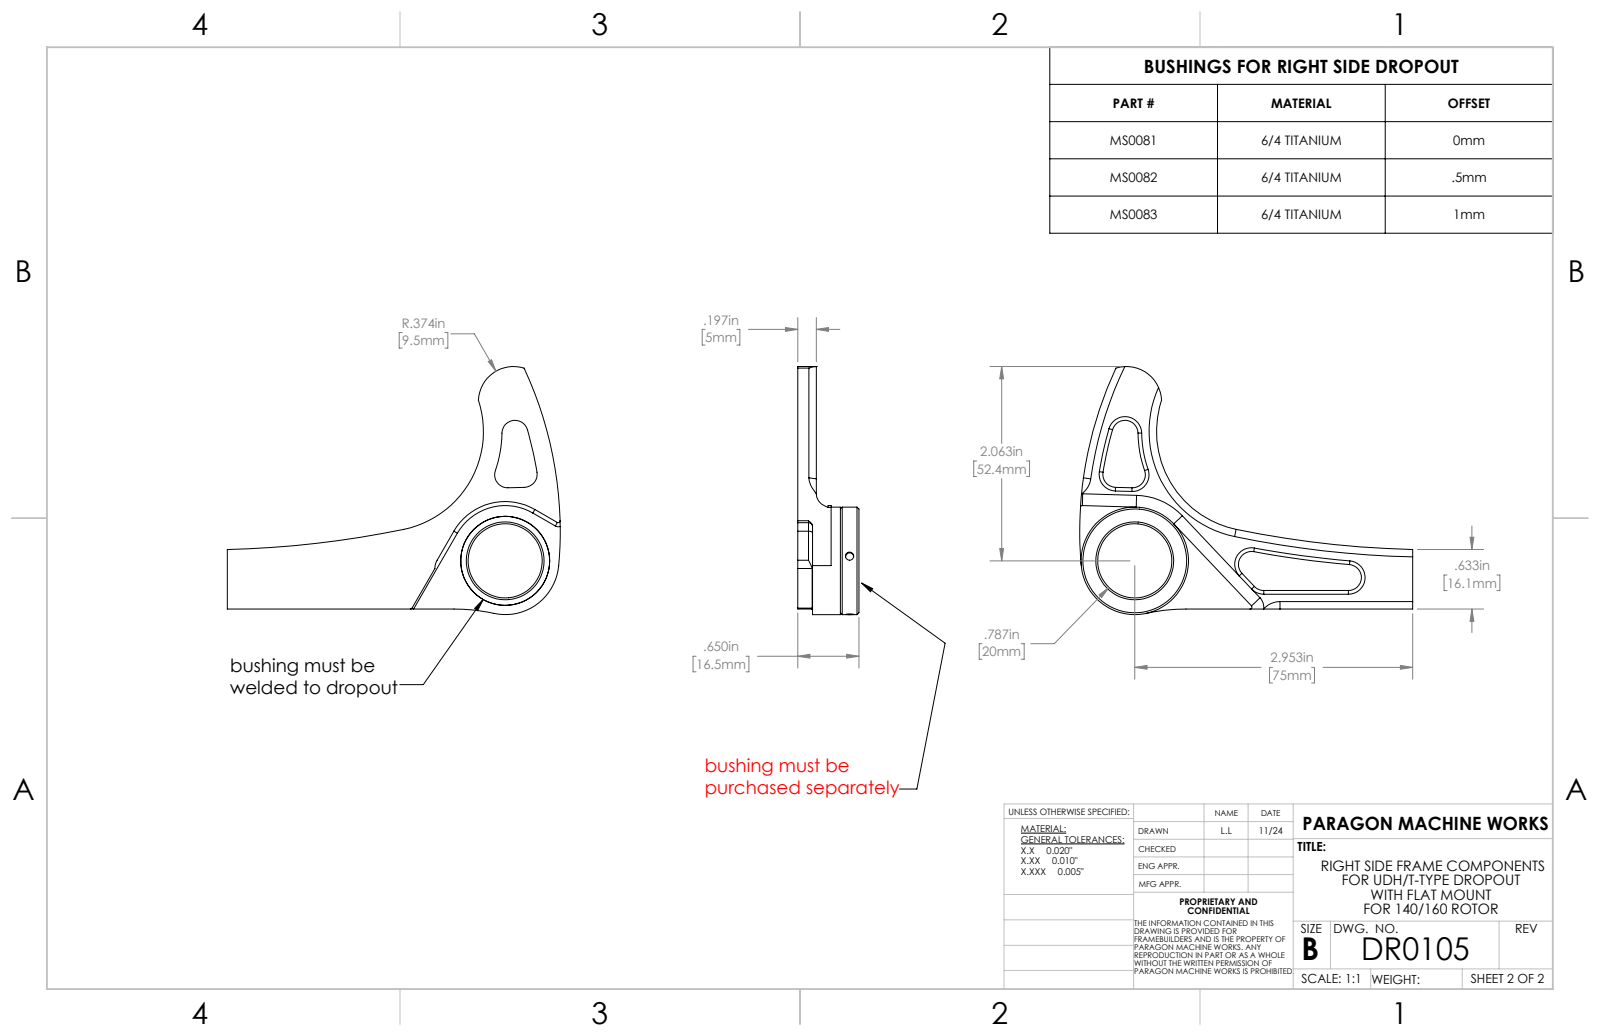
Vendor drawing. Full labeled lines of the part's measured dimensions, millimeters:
Part name (STEP PRODUCT): DR0102R
STEP written by: SolidWorks 2023 (AUTOMOTIVE_DESIGN)
Units: millimetres
Bodies: 1 solid, 74 faces (21 planar, 31 cylindrical, 22 other)
Overall size (bounding box): 89.85 × 66.91 × 11.5
Volume: 10 148 mm³ · Surface area: 6 802 mm²
Round holes (diameter × count): ⌀24 ×1
Round bosses / shafts (diameter × count): ⌀29 ×1
Partial cylindrical surfaces — rounded edges, fillets, slot ends (radius × count): R3.5 ×6, R0.5 ×4, R1.1 ×2, R3.18 ×2, R4.5 ×1, R9.5 ×1, R16 ×1, R26.95 ×1
Main face-to-face distances: 5, 1, 4, 3, 2, 9, 6, 11.5, 8.5, 7.5
